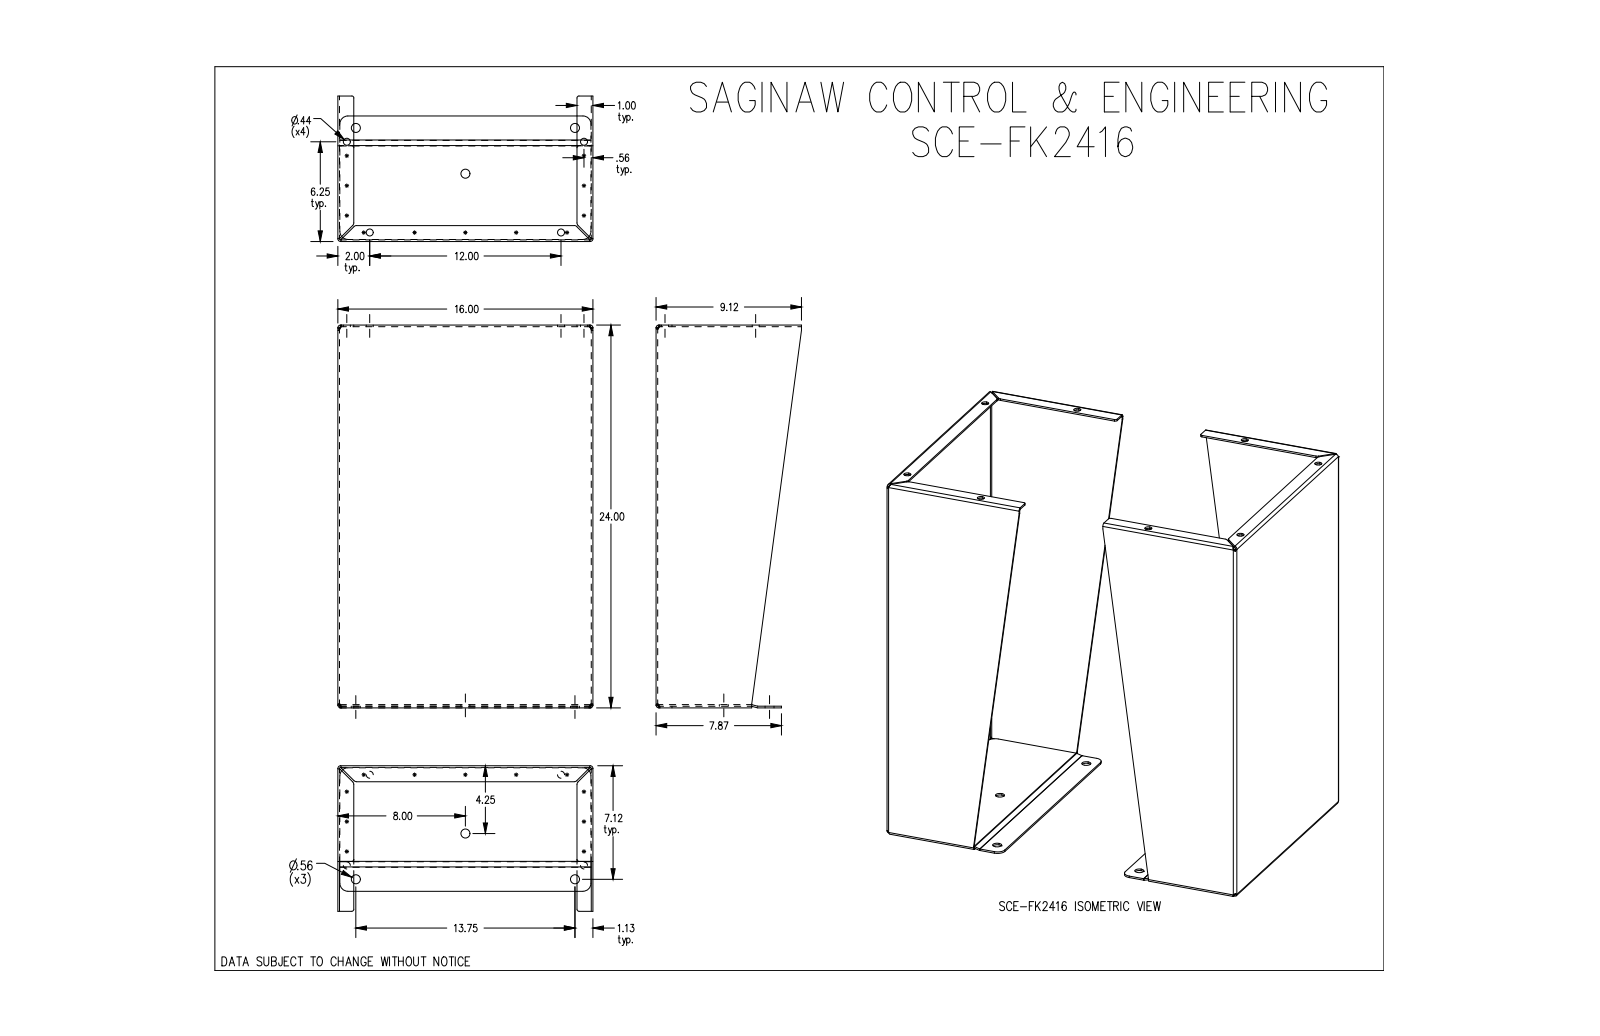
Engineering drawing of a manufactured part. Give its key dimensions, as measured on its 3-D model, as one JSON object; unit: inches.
{"part_name": "SCE-FK2416", "step_written_by": "SolidWorks 2019 (CONFIG_CONTROL_DESIGN)", "units": "inches", "bodies": {"solids": 4, "faces": 214, "planar": 96, "cylindrical": 86, "other": 32}, "overall_size": [24, 24, 16], "volume_in3": 189, "surface_area_in2": 3670, "round_holes": [[0.437, 8], [0.563, 6]], "partial_cylinders_radius": [[0.166, 16], [0.062, 14], [0.125, 8], [0.22, 8], [0.5, 8], [0.063, 2]], "face_to_face_distances": [0.104, 23.896, 15.896, 23.792, 24, 16, 15.792, 0.101, 23.893, 23.688], "hole_center_spacings": [1.035, 5.866, 6.614, 7.043, 7.449, 7.701, 10.646, 14.38]}
